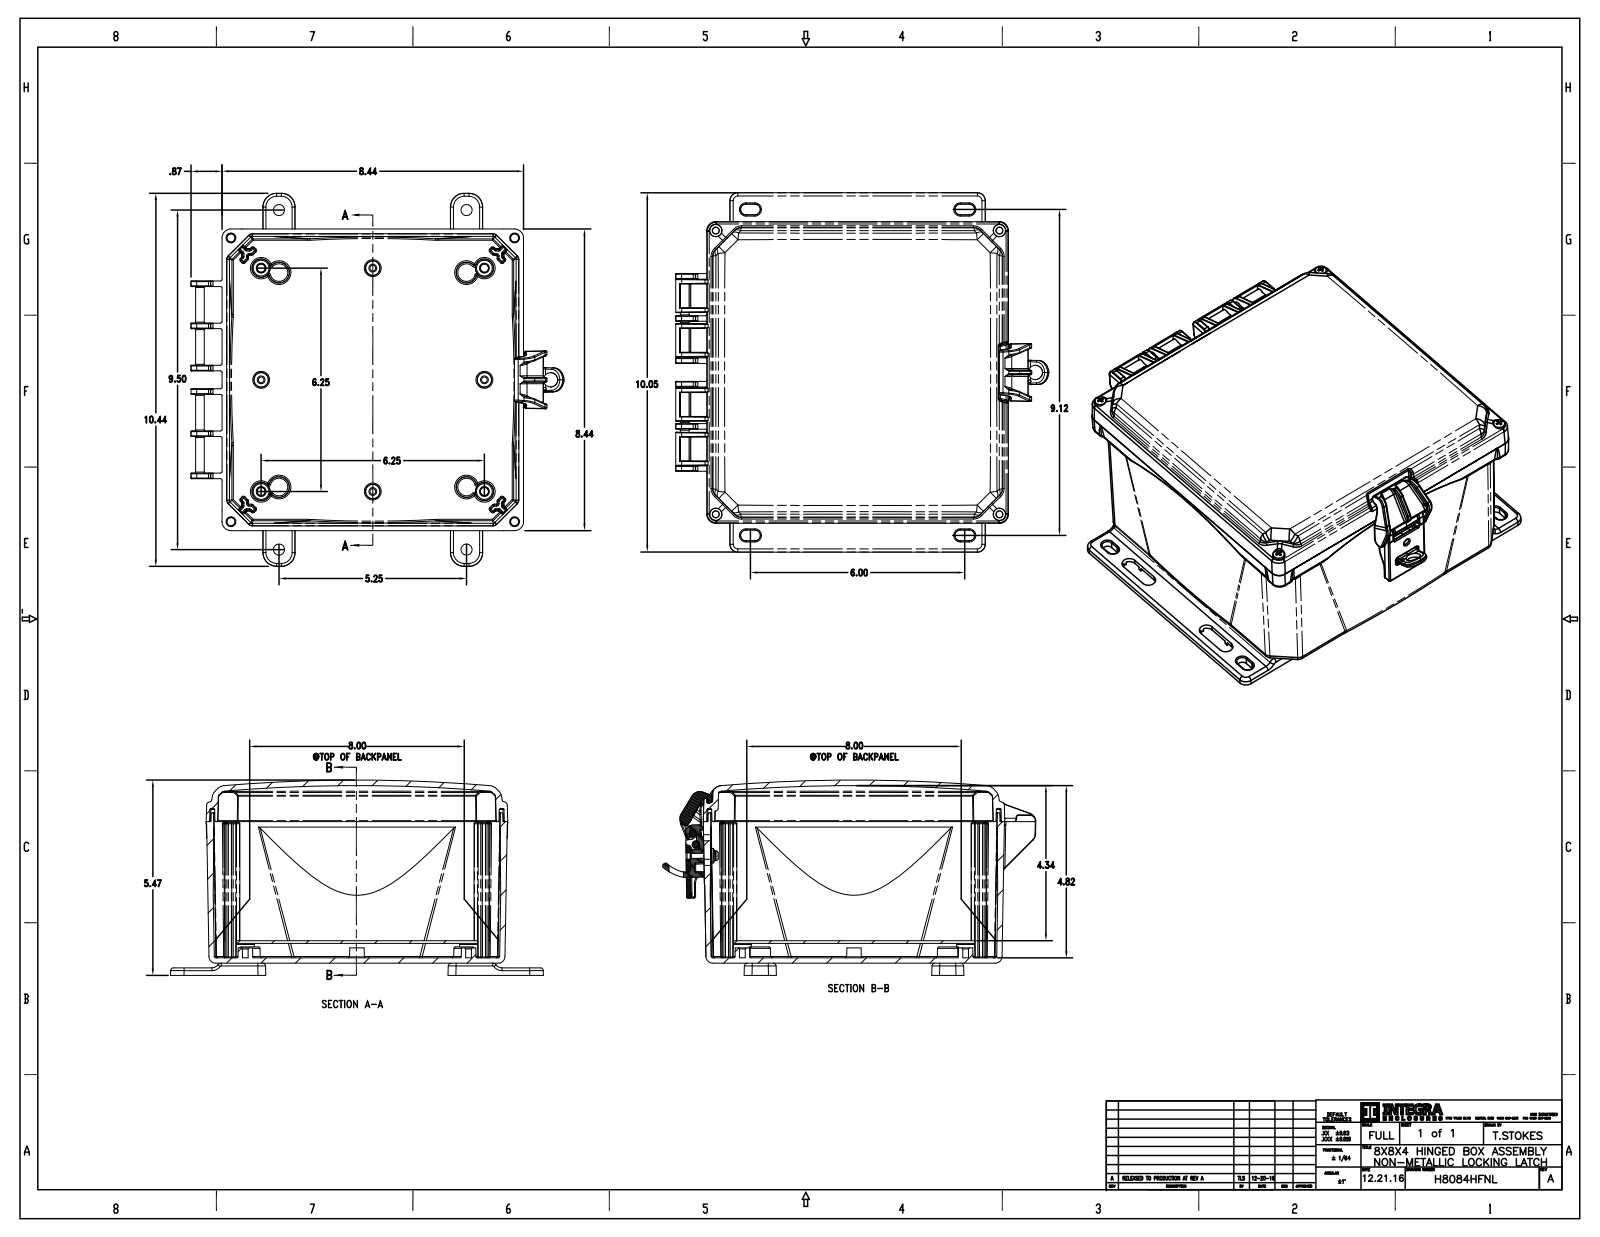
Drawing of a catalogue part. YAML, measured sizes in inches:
part_name: "H884BH; 9912525-80-10; 9912521-80-10; H884BH_ASM (+8 more)"
step_written_by: "CREO PARAMETRIC BY PTC INC, 2016050 (CONFIG_CONTROL_DESIGN)"
units: inches
bodies: {solids: 31, faces: 6348, planar: 2631, cylindrical: 1959, other: 1758}
overall_size: [10.445, 10.06, 5.465]
volume: 55.48
surface_area: 796.1
round_holes:
  - {diameter: 0.19, count: 8}
  - {diameter: 0.16, count: 4}
  - {diameter: 0.201, count: 4}
  - {diameter: 0.116, count: 2}
  - {diameter: 0.125, count: 2}
  - {diameter: 0.08, count: 1}
  - {diameter: 0.14, count: 1}
  - {diameter: 0.175, count: 1}
  - {diameter: 0.21, count: 1}
  - {diameter: 0.33, count: 1}
  - {diameter: 0.35, count: 1}
  - {diameter: 0.4, count: 1}
round_bosses_or_shafts:
  - {diameter: 0.25, count: 12}
  - {diameter: 0.3, count: 8}
  - {diameter: 0.298, count: 8}
  - {diameter: 0.29, count: 8}
  - {diameter: 0.26, count: 8}
  - {diameter: 0.258, count: 8}
  - {diameter: 0.375, count: 4}
  - {diameter: 0.372, count: 4}
partial_cylinders:
  - {radius: 0.03, count: 397}
  - {radius: 0.02, count: 102}
  - {radius: 0.015, count: 74}
  - {radius: 0.025, count: 64}
  - {radius: 0.09, count: 50}
  - {radius: 0.005, count: 48}
  - {radius: 0.04, count: 47}
  - {radius: 0.06, count: 42}
face_to_face_distances: [0.15, 0.12, 0.32, 0.27, 0.34, 0.225, 0.49, 0.13, 0.095, 0.22]
hole_center_spacings: [0.275, 3.125, 4.059, 6.988, 7.145, 8.13, 6.25, 0.516]
